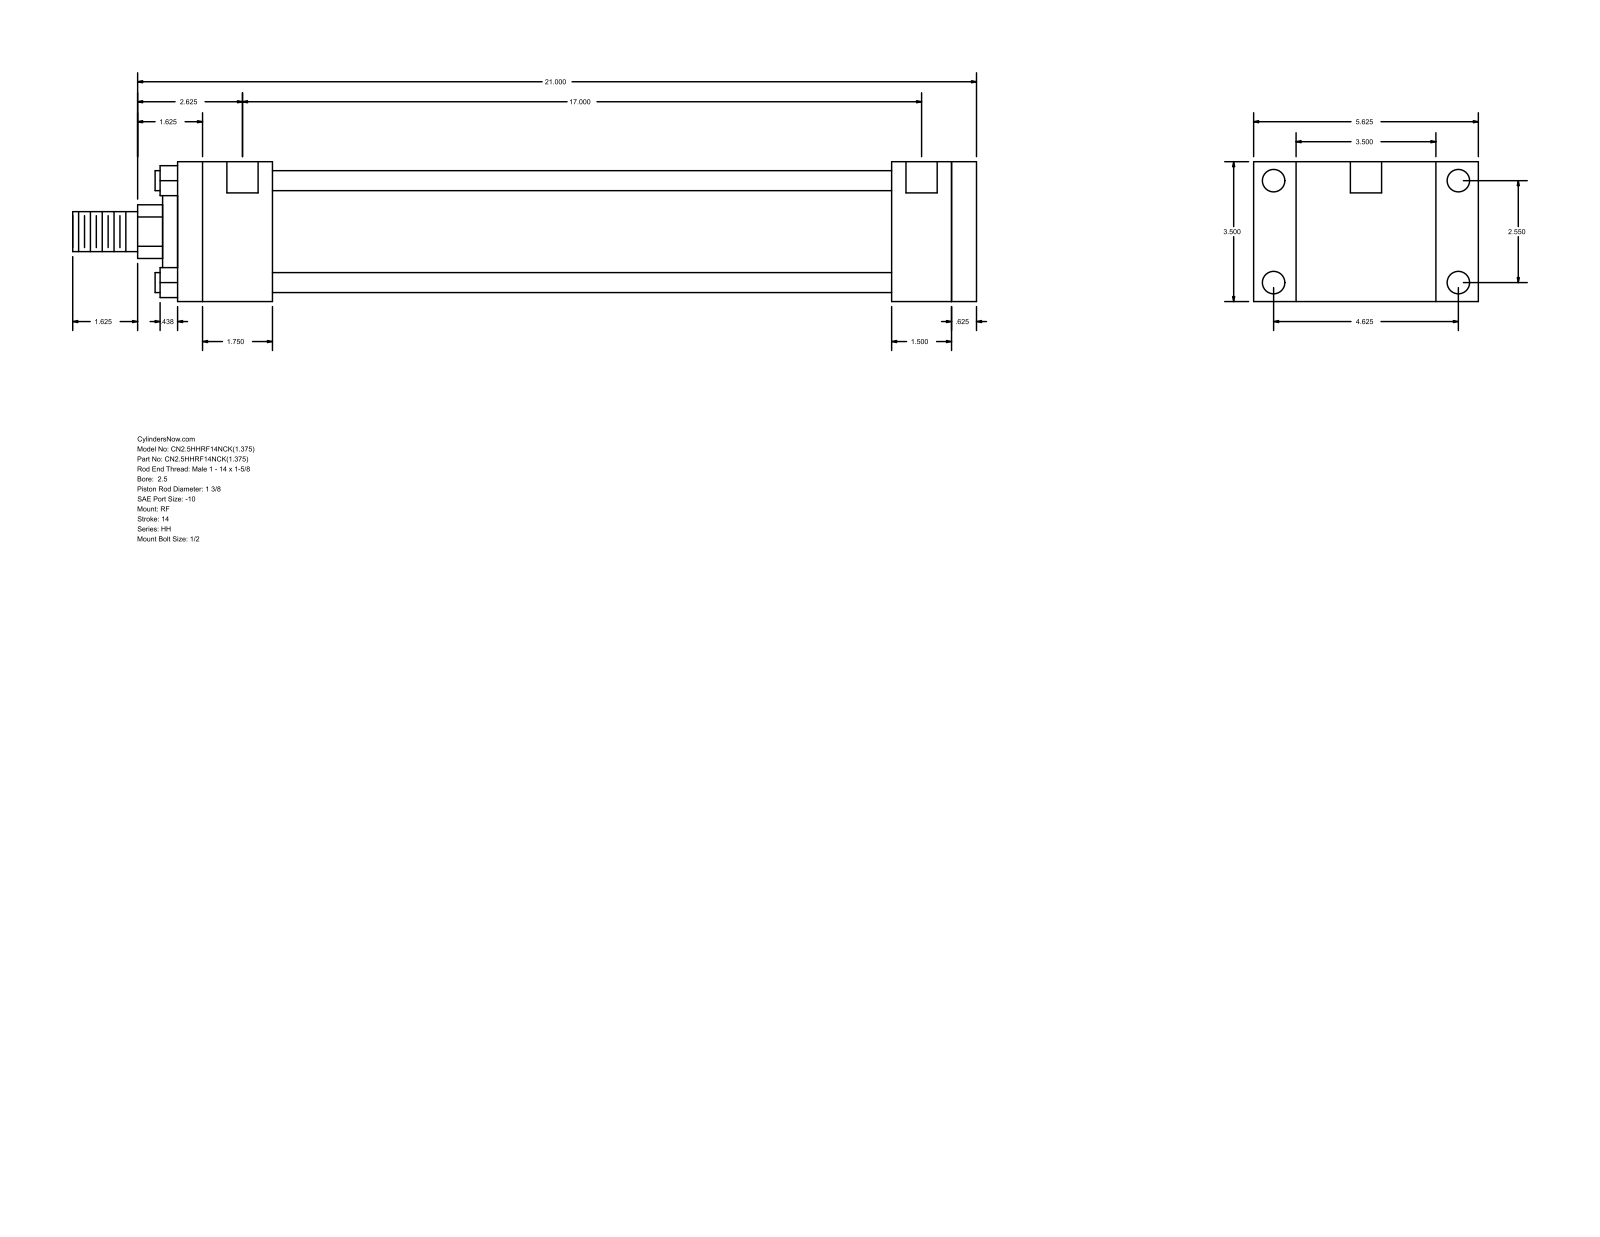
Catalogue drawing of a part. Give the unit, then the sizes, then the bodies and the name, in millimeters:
Units: millimetres
Overall size (bounding box): 574.67 × 142.88 × 88.9
Round holes (diameter × count): ⌀5.56 ×4, ⌀14.3 ×4, ⌀19.84 ×2
Round bosses / shafts (diameter × count): ⌀12.7 ×4, ⌀73.03 ×1, ⌀50.8 ×1, ⌀34.92 ×1, ⌀25.4 ×1
Partial cylindrical surfaces — rounded edges, fillets, slot ends (radius × count): R17.06 ×1
Main face-to-face distances: 88.9, 508, 15.88, 492.12, 53.97, 60.32, 431.8, 447.68, 454.03, 393.71
Hole centre spacings: 1.58, 64.76, 117.48, 134.15, 433.39, 434.97, 431.81
Bodies: 0 solids, 92 faces (64 planar, 28 cylindrical, 0 other)
Part name (STEP PRODUCT): HH_RF__0250_1.375
STEP written by: GSSL Pune (CONFIG_CONTROL_DESIGN)
